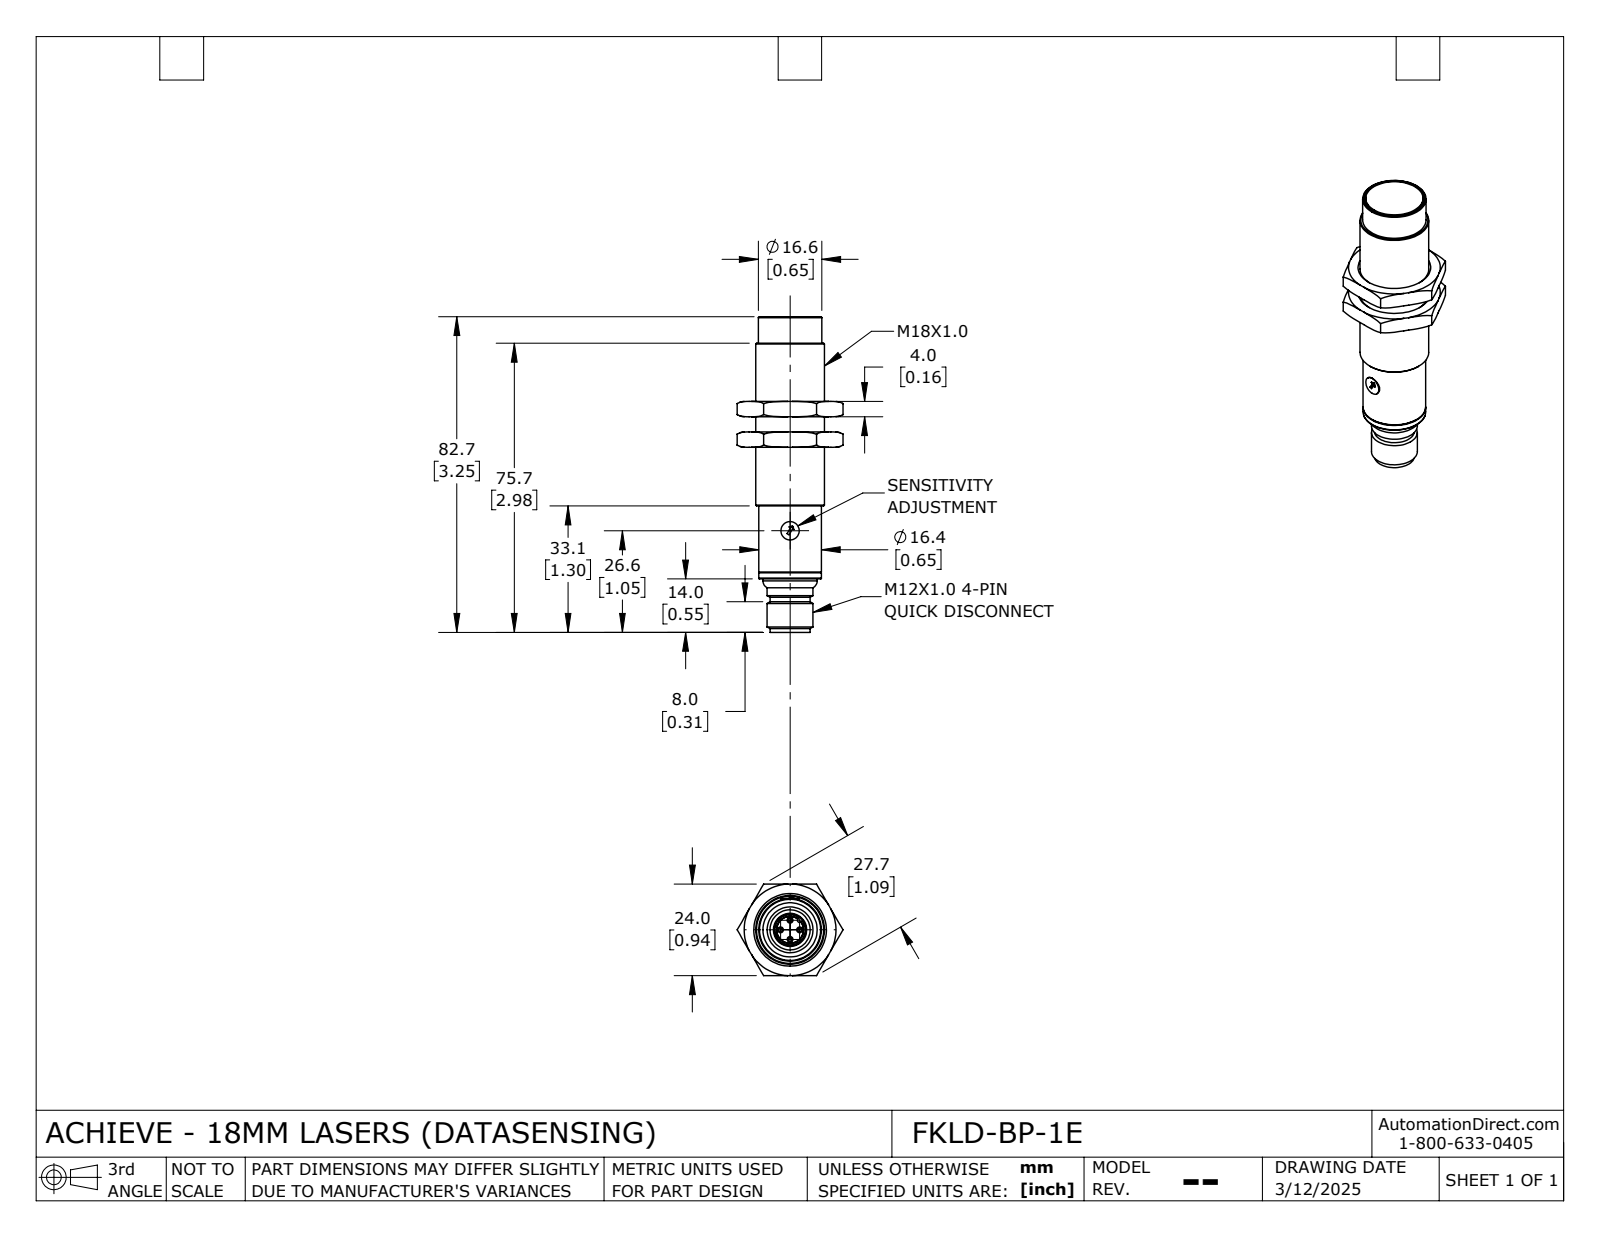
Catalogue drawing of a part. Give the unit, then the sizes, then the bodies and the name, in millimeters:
Units: millimetres
Overall size (bounding box): 82.7 × 27.7 × 24
Round holes (diameter × count): ⌀7.1 ×1, ⌀8.3 ×1, ⌀14.9 ×1, ⌀18 ×1
Round bosses / shafts (diameter × count): ⌀1 ×4, ⌀16.6 ×1, ⌀16.4 ×1, ⌀15 ×1, ⌀14.8 ×1, ⌀14.2 ×1, ⌀12 ×1, ⌀10.5 ×1
Partial cylindrical surfaces — rounded edges, fillets, slot ends (radius × count): R0.5 ×2, R7.5 ×2, R0.6 ×1, R1.3 ×1
Main face-to-face distances: 4, 8, 24, 2.4, 2.5, 27.6, 27.8, 30.2, 19.6, 19.8
Volume: 19 270 mm³ · Surface area: 8 148 mm²
Bodies: 3 solids, 127 faces (48 planar, 30 cylindrical, 49 other)
Part name (STEP PRODUCT): FKLD-BP-1E_Default
STEP written by: SolidWorks 2024 (CONFIG_CONTROL_DESIGN)
